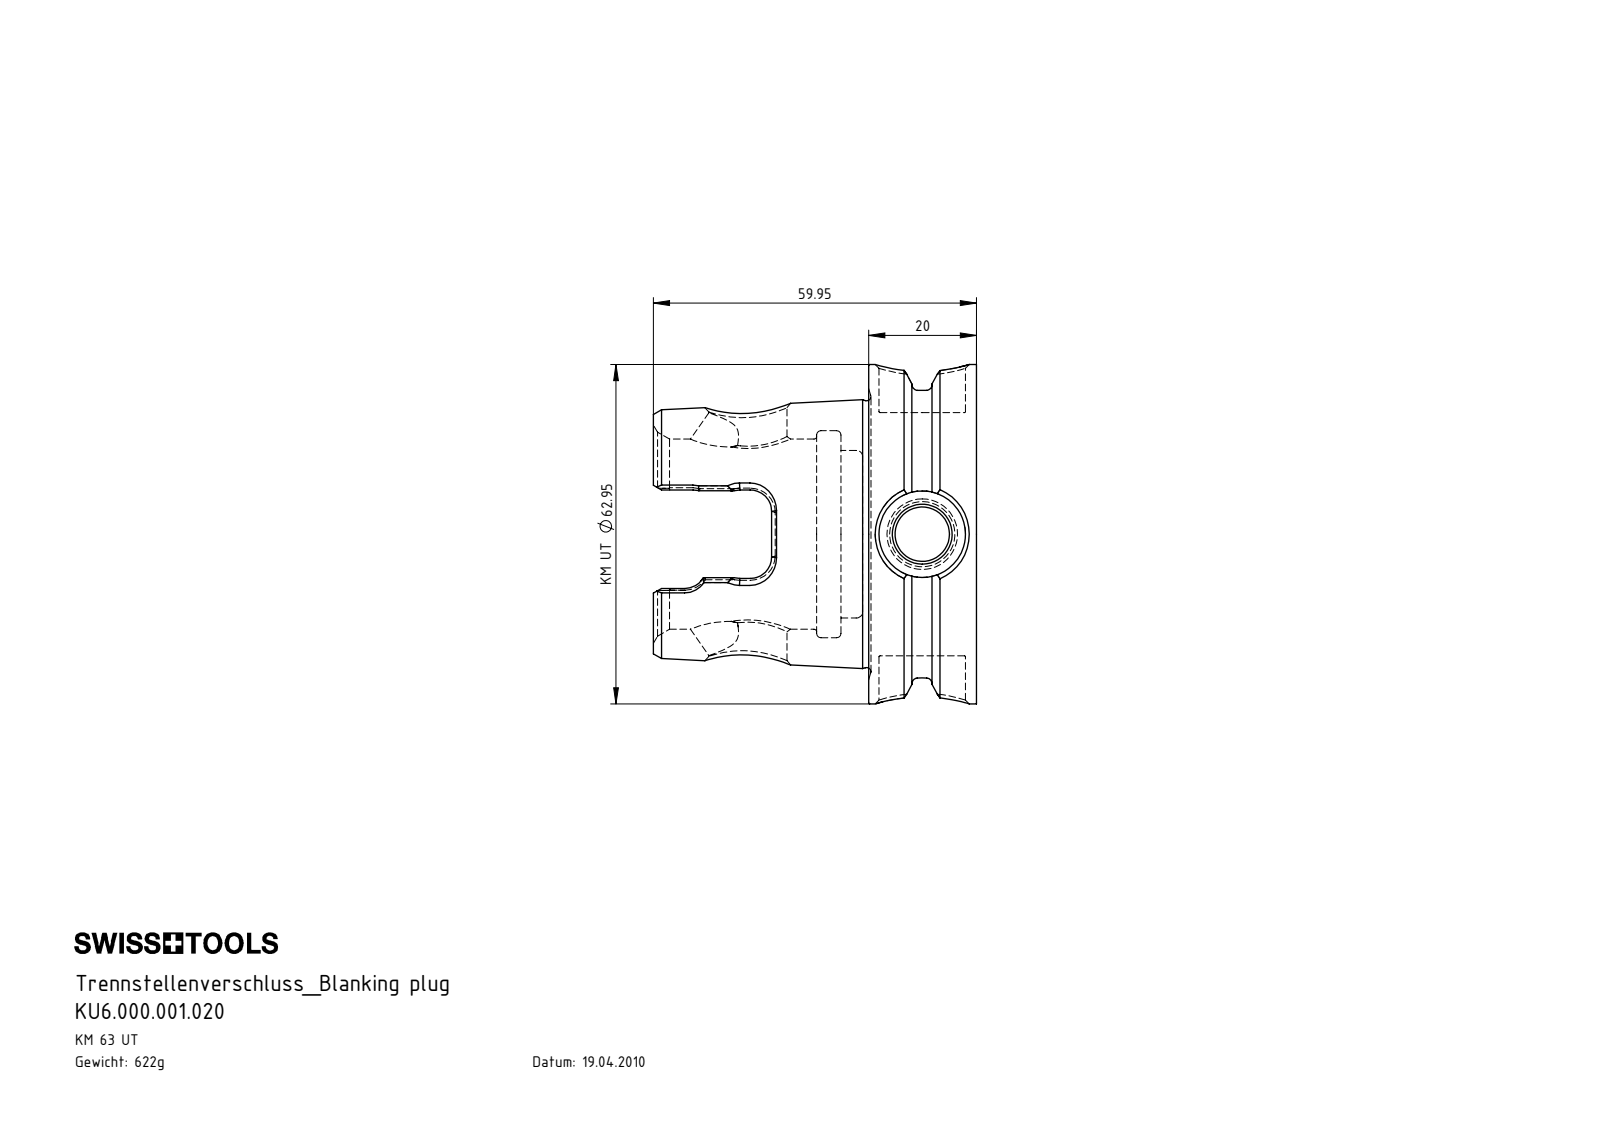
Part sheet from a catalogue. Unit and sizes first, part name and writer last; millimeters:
Units: millimetres
Overall size (bounding box): 62.95 × 62.95 × 59.95
Round holes (diameter × count): ⌀16.05 ×2, ⌀10.1 ×1, ⌀12.1 ×1, ⌀14.5 ×1, ⌀31.1 ×1, ⌀35.27 ×1, ⌀38.4 ×1
Round bosses / shafts (diameter × count): ⌀62.95 ×1
Partial cylindrical surfaces — rounded edges, fillets, slot ends (radius × count): R4 ×6, R7.04 ×2, R27.85 ×1
Main face-to-face distances: 20, 1.1, 21.1, 4.05, 5.15, 25.15, 45.1, 34.8, 38.85, 39.95
Hole centre spacings: 32.35
Volume: 79 167 mm³ · Surface area: 21 231 mm²
Bodies: 1 solid, 216 faces (50 planar, 46 cylindrical, 120 other)
Part name (STEP PRODUCT): KU6.000.001.020
STEP written by: SolidWorks 2017 (CONFIG_CONTROL_DESIGN)
